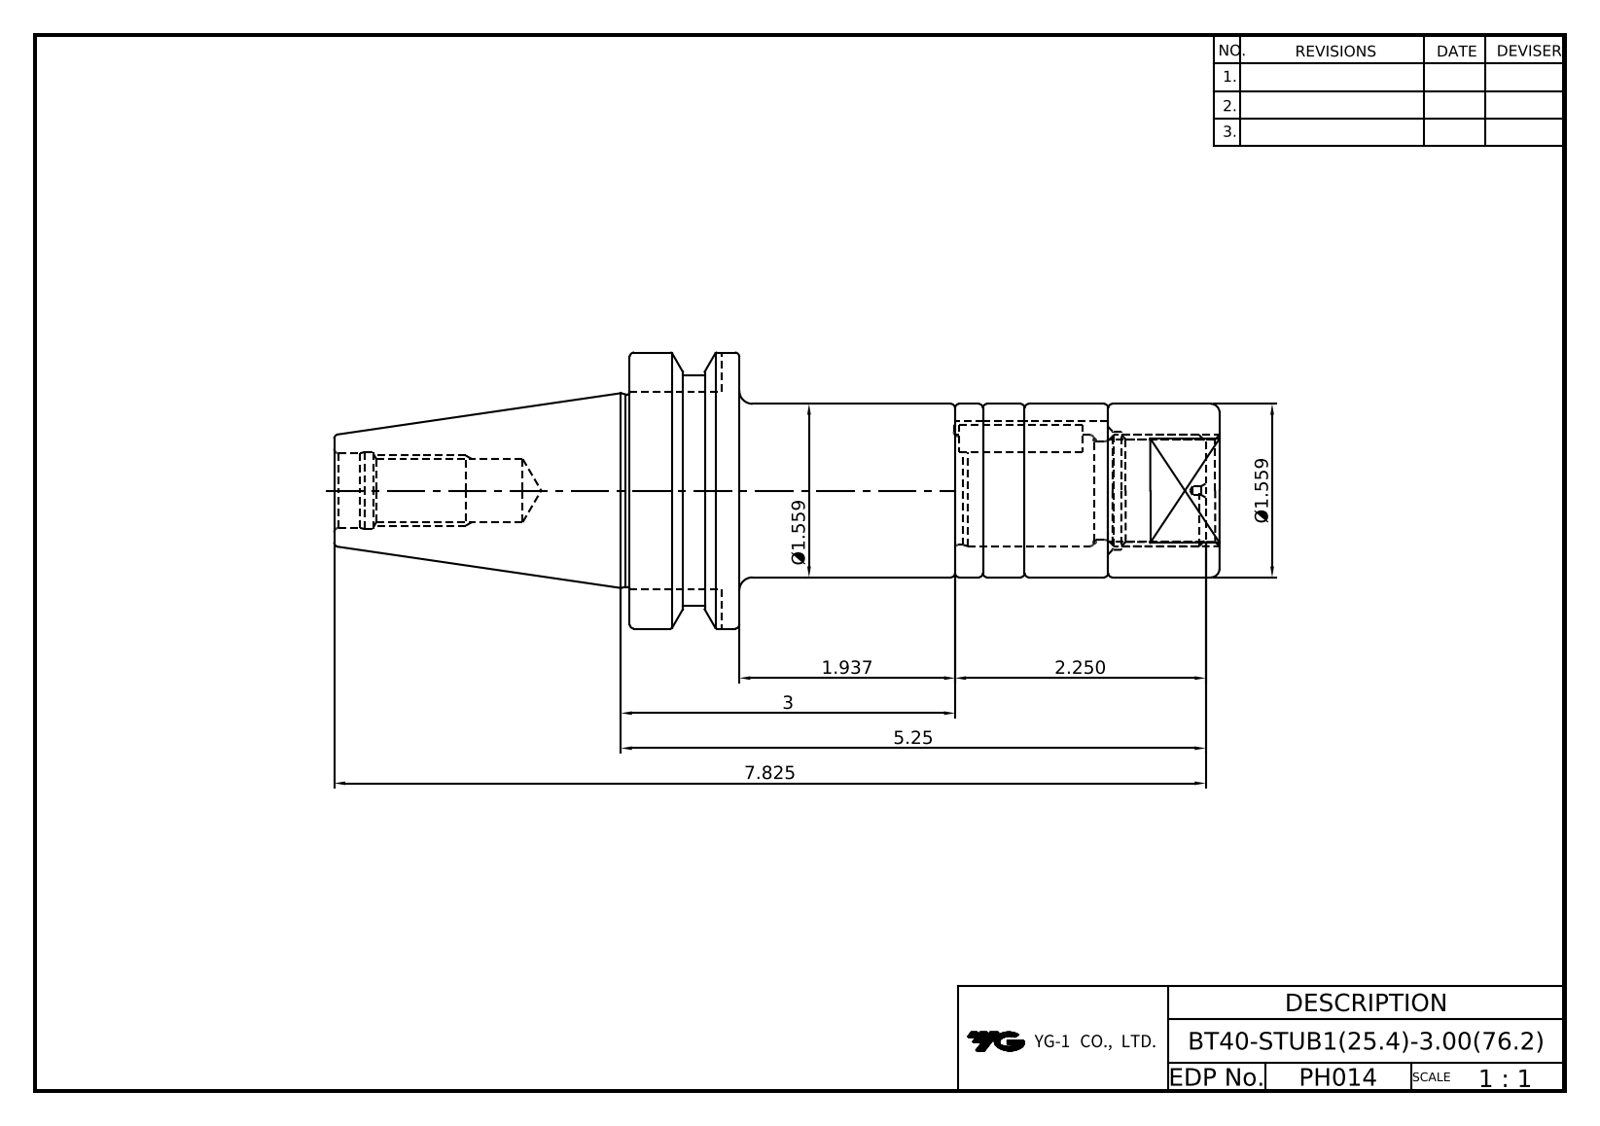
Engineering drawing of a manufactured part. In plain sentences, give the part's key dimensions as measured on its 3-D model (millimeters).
The part is named "BT40-STUB25.4-76.2; BT40-STUB25.4-76.2(20240129); 6.35x6.35x25(25.4용)-KEY; 0.25(6.35)-SPACER (+3 more)". Its 3-D file was written by "Autodesk Inventor 2024 (AUTOMOTIVE_DESIGN)". It is 6 solids with 109 faces: 43 planar, 29 cylindrical and 37 other. Overall it measures 201.93 by 63 by 63 millimeters. Its volume is 260 530 cubic millimeters and its surface area 49 592 square millimeters. Round holes: 1 of diameter 13.84, 1 of diameter 17, 1 of diameter 17.6, 1 of diameter 23.11, 1 of diameter 25.4, 1 of diameter 27. Round bosses or shafts: 1 of diameter 63, 1 of diameter 52.6, 1 of diameter 44, 1 of diameter 39.6, 1 of diameter 24.8, 1 of diameter 22.4. Partial cylindrical surfaces (rounded edges, fillets, slot ends): 2 of radius 3.17, 1 of radius 8.05. The main face-to-face distances are 25, 80.55, 55.55, 6.35, 109.12, 84.12, 28.57, 74.2, 49.2, 34.92.
